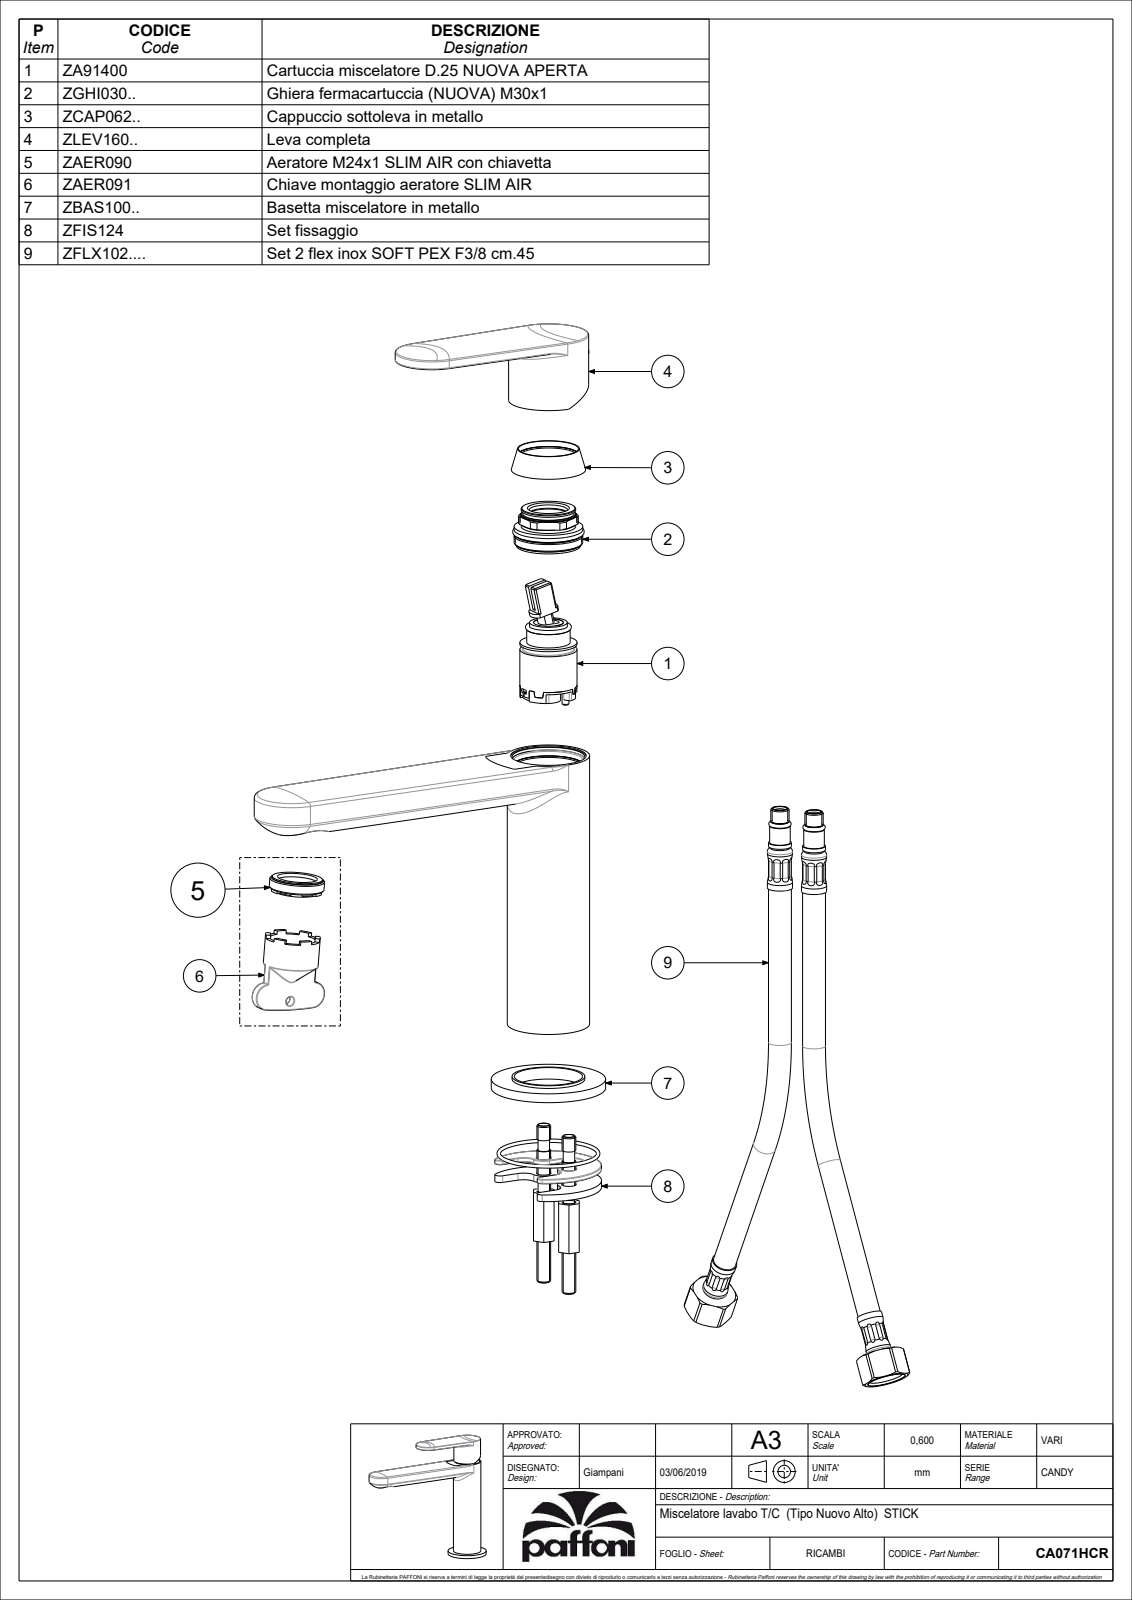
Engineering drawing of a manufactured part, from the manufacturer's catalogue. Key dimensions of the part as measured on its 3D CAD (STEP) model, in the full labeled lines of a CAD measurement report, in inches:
Part name (STEP PRODUCT): CA071HCR
STEP written by: CREO PARAMETRIC BY PTC INC, 2020044 (CONFIG_CONTROL_DESIGN)
Units: inches
Bodies: 1 solid, 1075 faces (248 planar, 369 cylindrical, 458 other)
Overall size (bounding box): 6.732 × 6.198 × 1.969
Volume: 7.784 in³ · Surface area: 120.6 in²
Round holes (diameter × count): ⌀0.197 ×2, ⌀0.217 ×2, ⌀0.276 ×2, ⌀0.339 ×2, ⌀0.37 ×2, ⌀0.118 ×1, ⌀0.165 ×1, ⌀0.63 ×1, ⌀0.657 ×1, ⌀0.689 ×1, ⌀0.756 ×1, ⌀0.795 ×1
Round bosses / shafts (diameter × count): ⌀0.157 ×2, ⌀1.969 ×1, ⌀1.646 ×1, ⌀1.417 ×1, ⌀1.378 ×1, ⌀1.252 ×1, ⌀1.24 ×1, ⌀1.181 ×1
Partial cylindrical surfaces — rounded edges, fillets, slot ends (radius × count): R0.02 ×64, R0.039 ×21, R0.028 ×10, R0.031 ×6, R0.118 ×6, R0.024 ×4, R0.026 ×4, R0.033 ×4
Main face-to-face distances: 0.138, 0.157, 0.039, 0.098, 0.02, 0.059, 4.941, 6.08, 5.922, 0.118
Hole centre spacings: 0.433, 0.06, 0.265, 0.303, 0.383, 0.423, 0.461, 0.513
